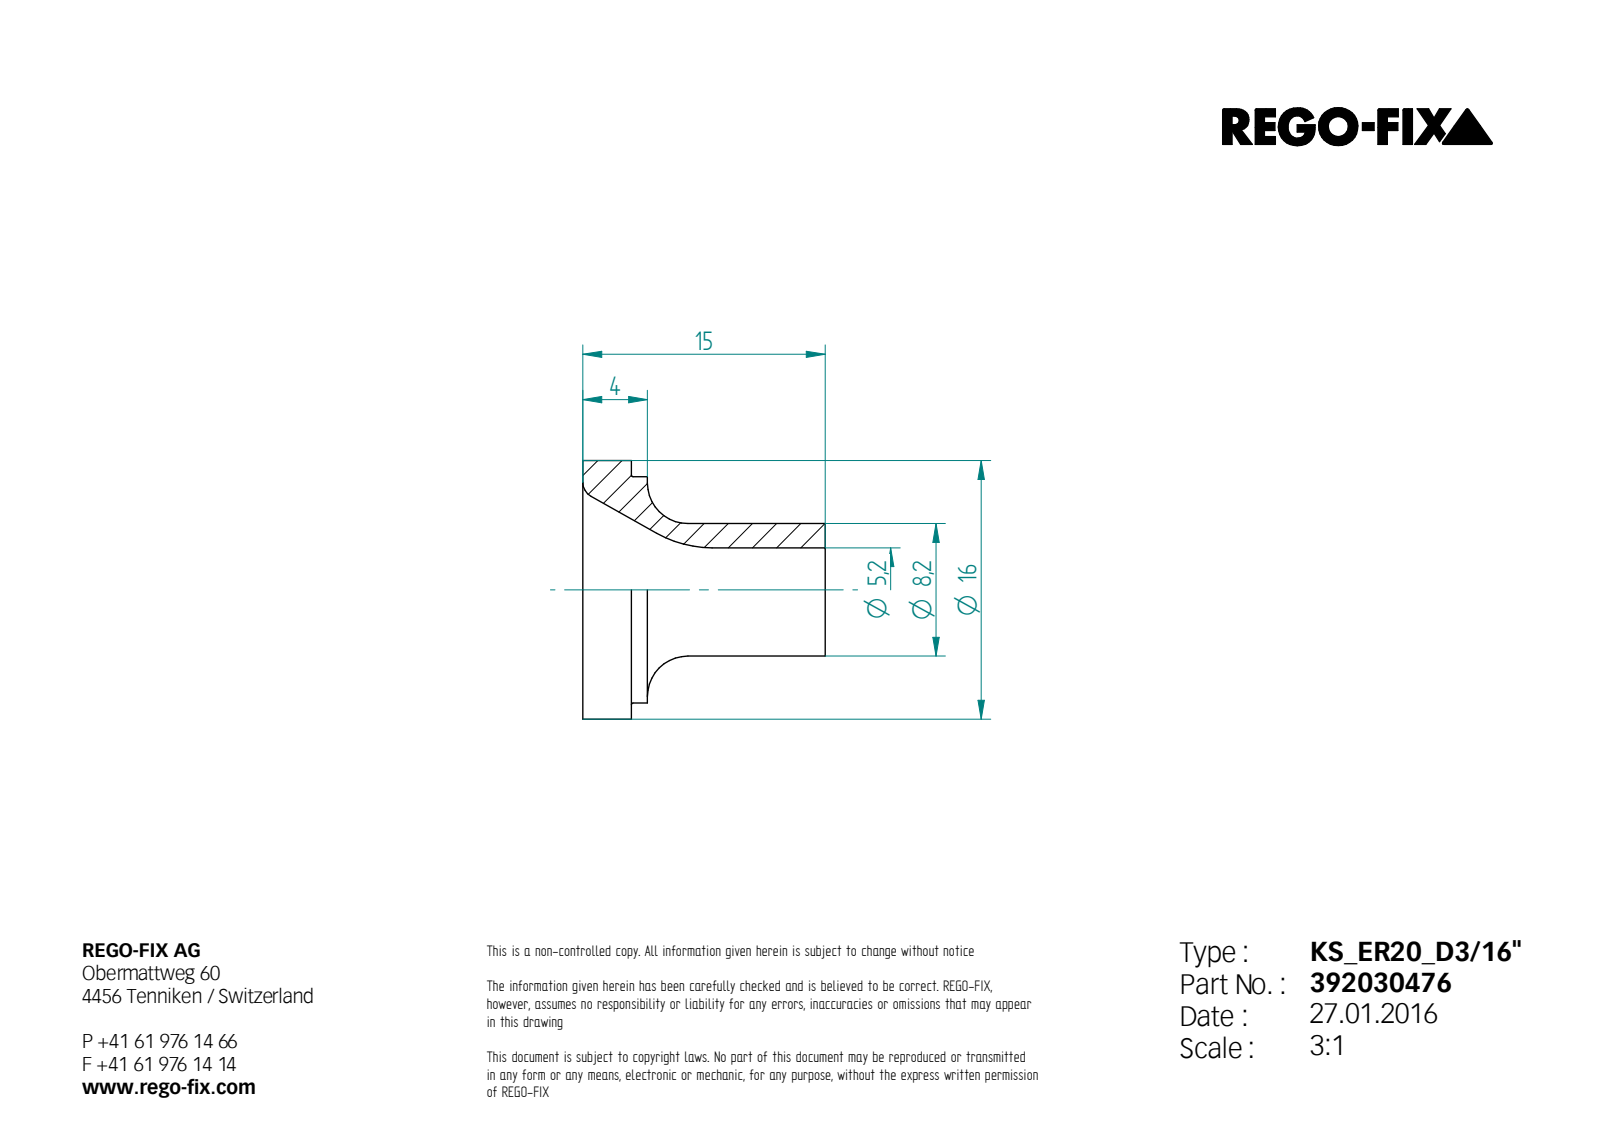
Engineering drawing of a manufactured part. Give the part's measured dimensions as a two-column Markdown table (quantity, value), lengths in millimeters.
| quantity | value |
| --- | --- |
| STEP written by | Unknown (AUTOMOTIVE_DESIGN) |
| units | millimeters |
| bodies | 1 solid, 13 faces (4 planar, 4 cylindrical, 5 other) |
| overall size | 16 × 16 × 15 |
| volume | 800 mm³ |
| surface area | 1 050 mm² |
| round holes (diameter × count) | 5.2 × 1 |
| round bosses / shafts (diameter × count) | 16 × 1, 14 × 1, 8.2 × 1 |
| main face-to-face distances | 3, 15, 12, 4, 1, 11 |
